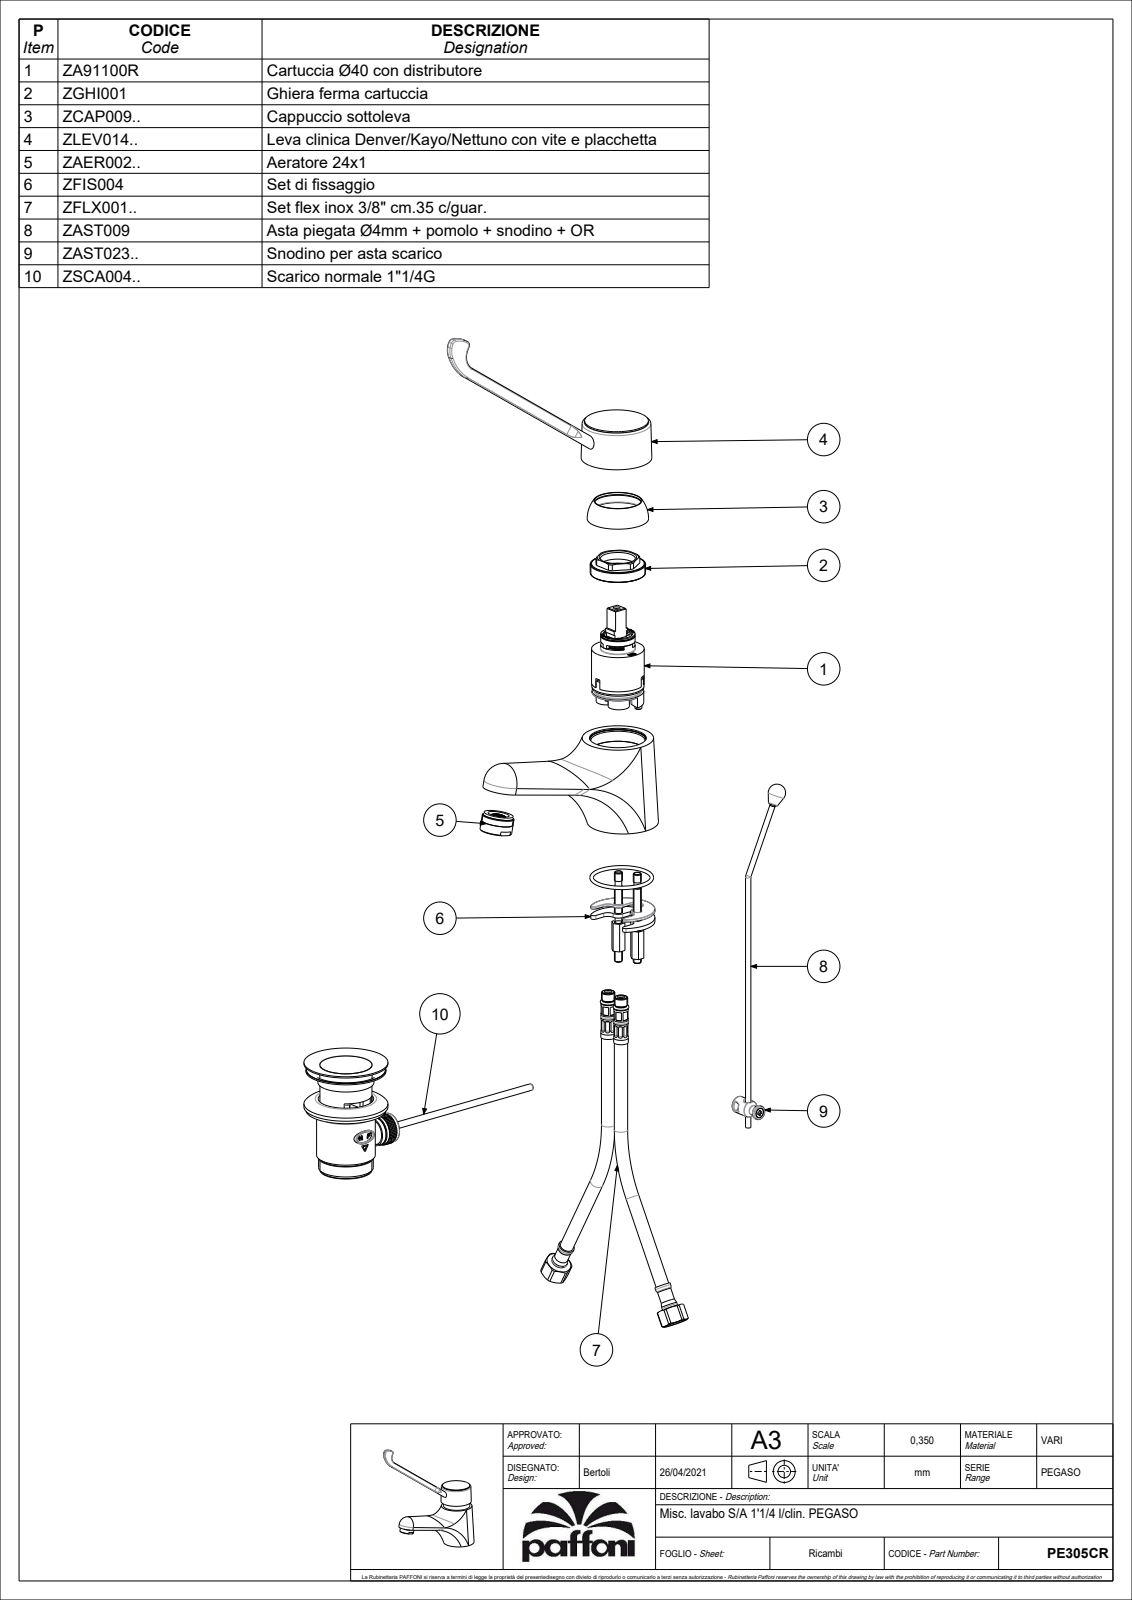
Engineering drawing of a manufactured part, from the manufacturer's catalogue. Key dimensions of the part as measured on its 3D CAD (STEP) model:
Part name (STEP PRODUCT): PE305CR_SW0001
STEP written by: CREO PARAMETRIC BY PTC INC, 2022124 (CONFIG_CONTROL_DESIGN)
Units: millimetres
Bodies: 3 solids, 2182 faces (1859 planar, 117 cylindrical, 206 other)
Overall size (bounding box): 211.88 × 208.58 × 53.5
Volume: 179 281 mm³ · Surface area: 75 361 mm²
Round holes (diameter × count): ⌀5.5 ×5, ⌀7 ×2, ⌀9 ×2, ⌀11 ×2, ⌀4 ×1, ⌀5 ×1, ⌀16 ×1, ⌀17 ×1, ⌀20 ×1, ⌀21 ×1, ⌀23 ×1, ⌀24.5 ×1
Round bosses / shafts (diameter × count): ⌀10 ×2, ⌀47.85 ×1, ⌀42 ×1, ⌀33 ×1, ⌀24 ×1, ⌀20.9 ×1, ⌀19.5 ×1, ⌀18.8 ×1
Partial cylindrical surfaces — rounded edges, fillets, slot ends (radius × count): R0.3 ×4, R1.5 ×2, R2 ×2, R6.5 ×2, R7.5 ×2, R18.3 ×2, R25.63 ×2, R0.5 ×1
Main face-to-face distances: 3.5, 6, 3, 4.5, 55.5, 4, 15.5, 77, 40, 22
Hole centre spacings: 1.12, 3.16, 8.6, 9.6, 9.9, 10.97, 12.08, 12.65
